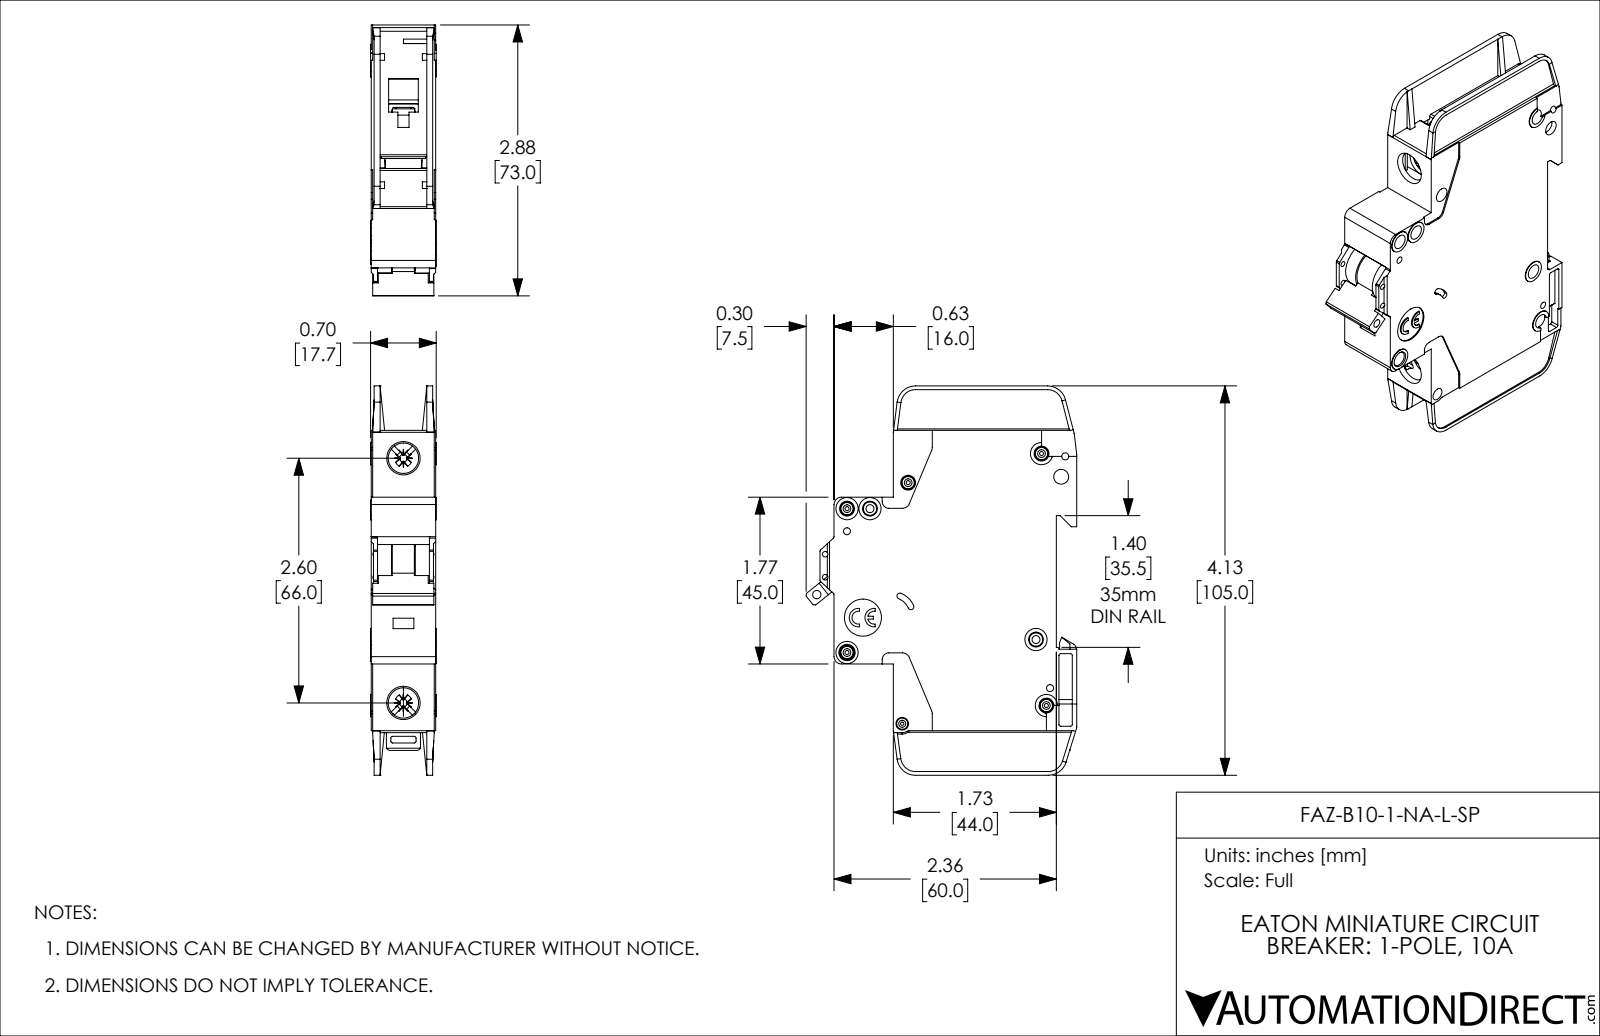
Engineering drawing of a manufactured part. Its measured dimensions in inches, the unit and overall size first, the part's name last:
Units: inches
Overall size (bounding box): 4.134 × 2.876 × 0.697
Round holes (diameter × count): ⌀0.157 ×8, ⌀0.043 ×5, ⌀0.075 ×4, ⌀0.059 ×2, ⌀0.085 ×2, ⌀0.323 ×2, ⌀0.035 ×1, ⌀0.089 ×1, ⌀0.098 ×1, ⌀0.134 ×1, ⌀0.394 ×1
Round bosses / shafts (diameter × count): ⌀0.13 ×5, ⌀0.236 ×4, ⌀0.118 ×2, ⌀0.098 ×1
Partial cylindrical surfaces — rounded edges, fillets, slot ends (radius × count): R0.02 ×42, R0.016 ×10, R0.039 ×10, R0.079 ×8, R0.197 ×5, R0.008 ×4, R0.026 ×4, R0.043 ×4
Main face-to-face distances: 0.047, 0.685, 0.591, 0.638, 0.094, 0.543, 0.016, 0.031, 0.496, 0.575
Hole centre spacings: 0.244, 0.537, 0.87, 0.189, 0.199, 0.204, 0.221, 0.24
Volume: 4.682 in³ · Surface area: 41.01 in²
Bodies: 1 solid, 1127 faces (671 planar, 357 cylindrical, 99 other)
Part name (STEP PRODUCT): FAZ-B10-1-NA-L-SP
STEP written by: SolidWorks 2019 (AUTOMOTIVE_DESIGN)
